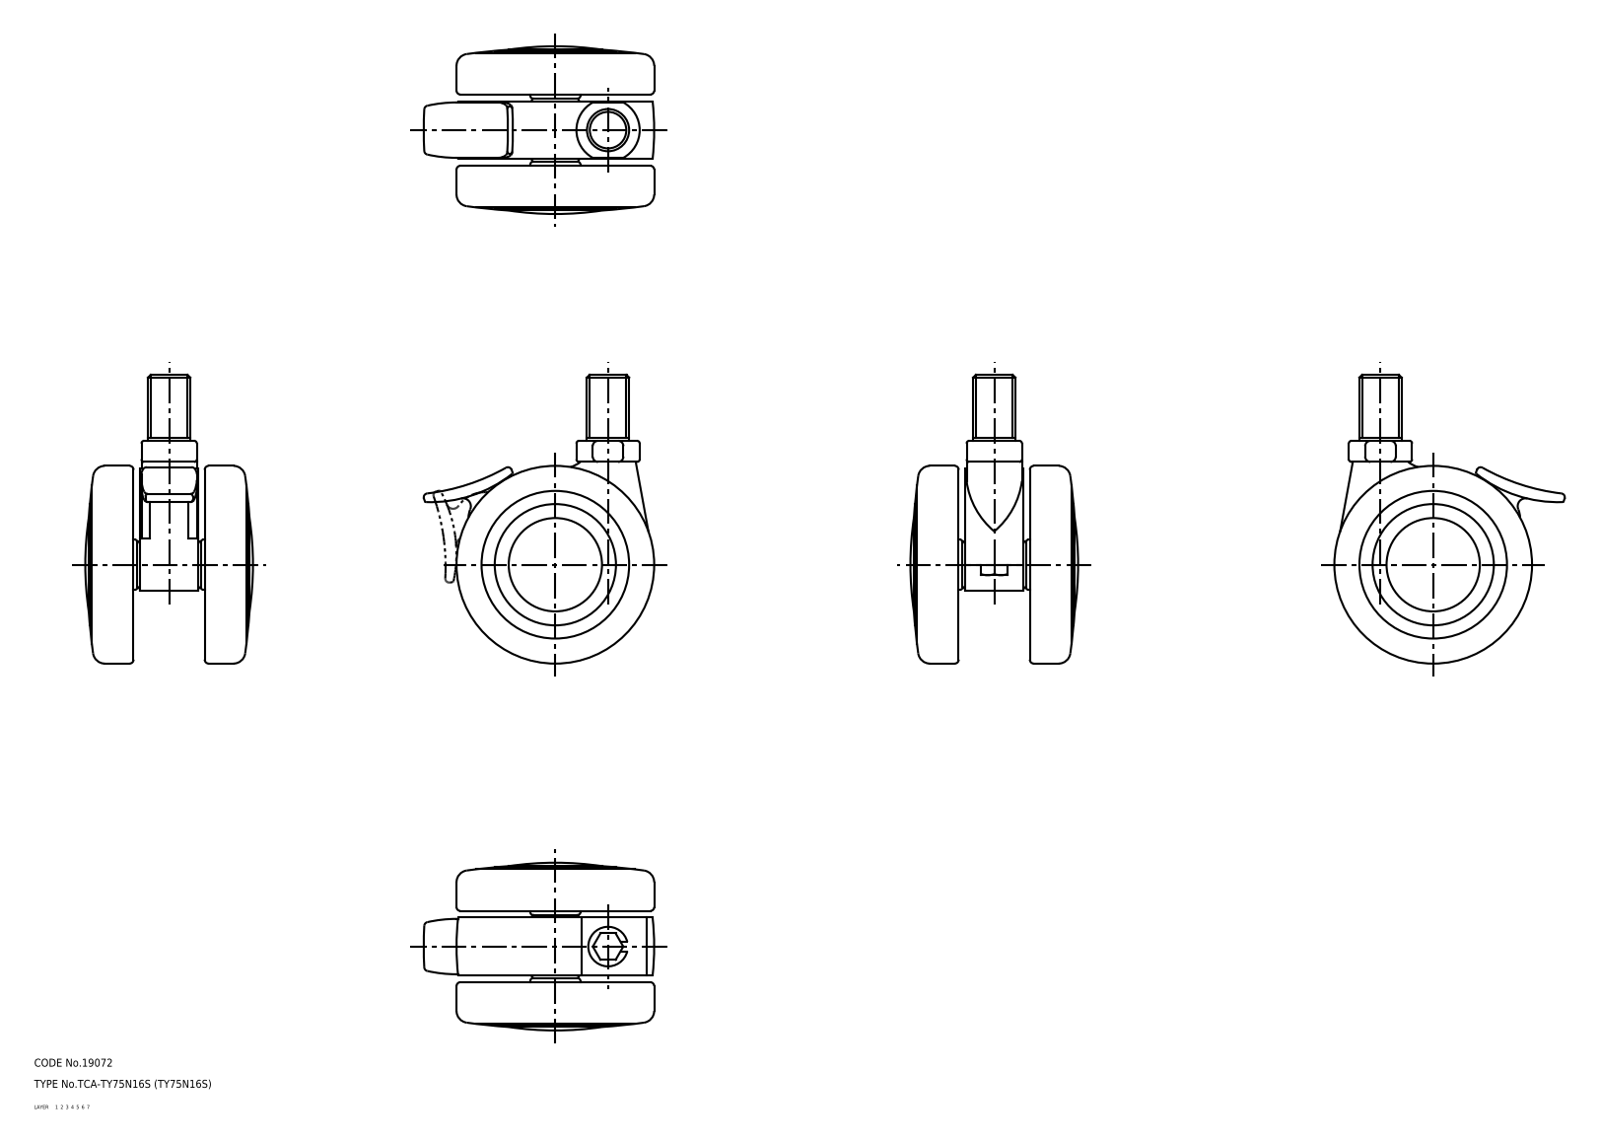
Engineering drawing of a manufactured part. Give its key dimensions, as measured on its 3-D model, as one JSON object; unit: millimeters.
{"part_name": "lever; wheel_mr; wheel; main shaft (+1 more)", "step_written_by": "CADfix (AUTOMOTIVE_DESIGN)", "units": "millimeters", "bodies": {"solids": 5, "faces": 198, "planar": 0, "cylindrical": 0, "other": 198}, "overall_size": [109.5, 87.44, 63.62], "volume_mm3": 192804, "surface_area_mm2": 53102}
